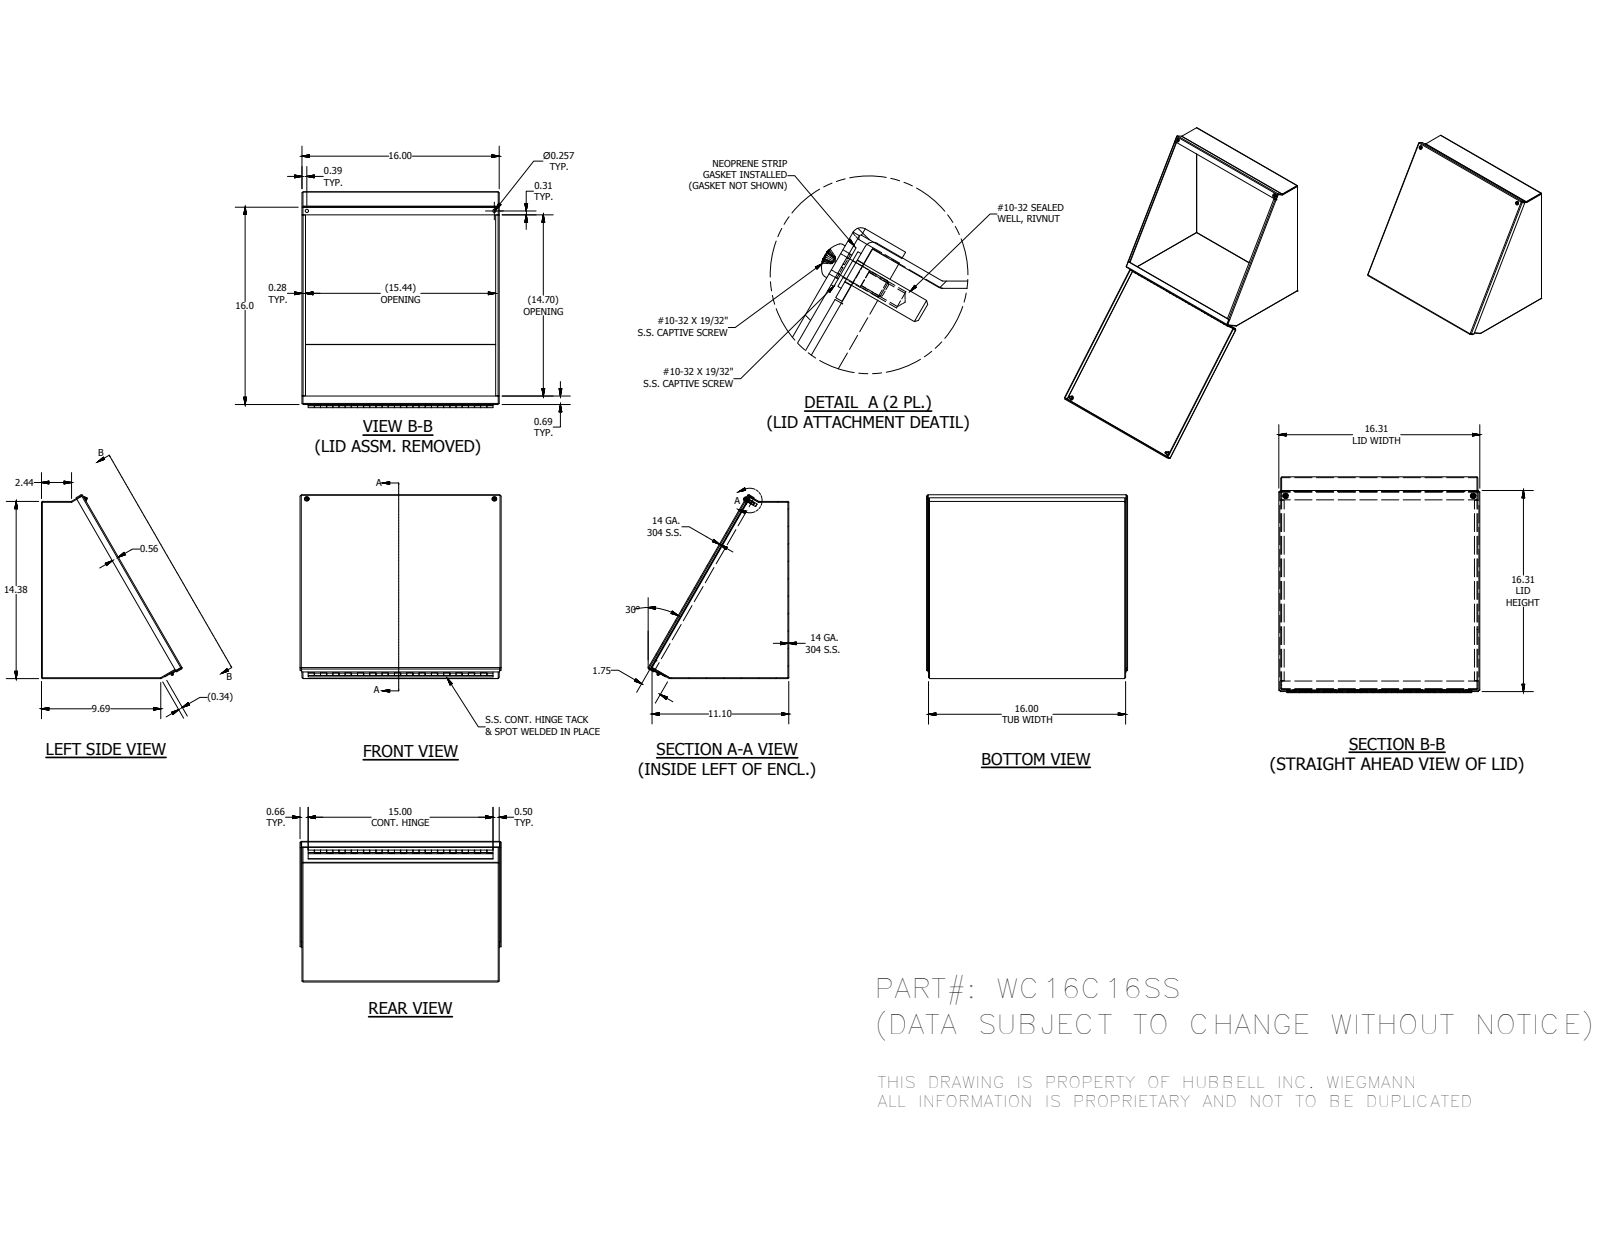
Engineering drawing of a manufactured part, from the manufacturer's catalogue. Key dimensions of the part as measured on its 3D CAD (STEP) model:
Part name (STEP PRODUCT): WC16C16SSBTB; WC16C16SSLID; WC16CSSLS; WC16CSSRS (+8 more)
STEP written by: Autodesk Inventor 2014 (AUTOMOTIVE_DESIGN)
Units: millimetres
Bodies: 13 solids, 447 faces (282 planar, 113 cylindrical, 52 other)
Overall size (bounding box): 414.34 × 378.86 × 289.89
Volume: 1 222 000 mm³ · Surface area: 1 331 000 mm²
Round holes (diameter × count): ⌀3.96 ×2, ⌀4.98 ×2, ⌀6.53 ×2, ⌀7.06 ×2, ⌀7.14 ×2, ⌀2.96 ×1
Round bosses / shafts (diameter × count): ⌀11.51 ×2, ⌀10.31 ×2, ⌀9.47 ×2, ⌀6.3 ×2, ⌀4.83 ×2, ⌀5.08 ×1, ⌀2.54 ×1
Partial cylindrical surfaces — rounded edges, fillets, slot ends (radius × count): R0.4 ×12, R2.28 ×12, R2.27 ×2
Main face-to-face distances: 1.88, 404.52, 402.64, 406.4, 363.25, 361.37, 1.87, 365.12, 363.24, 3.97
Hole centre spacings: 386.74
